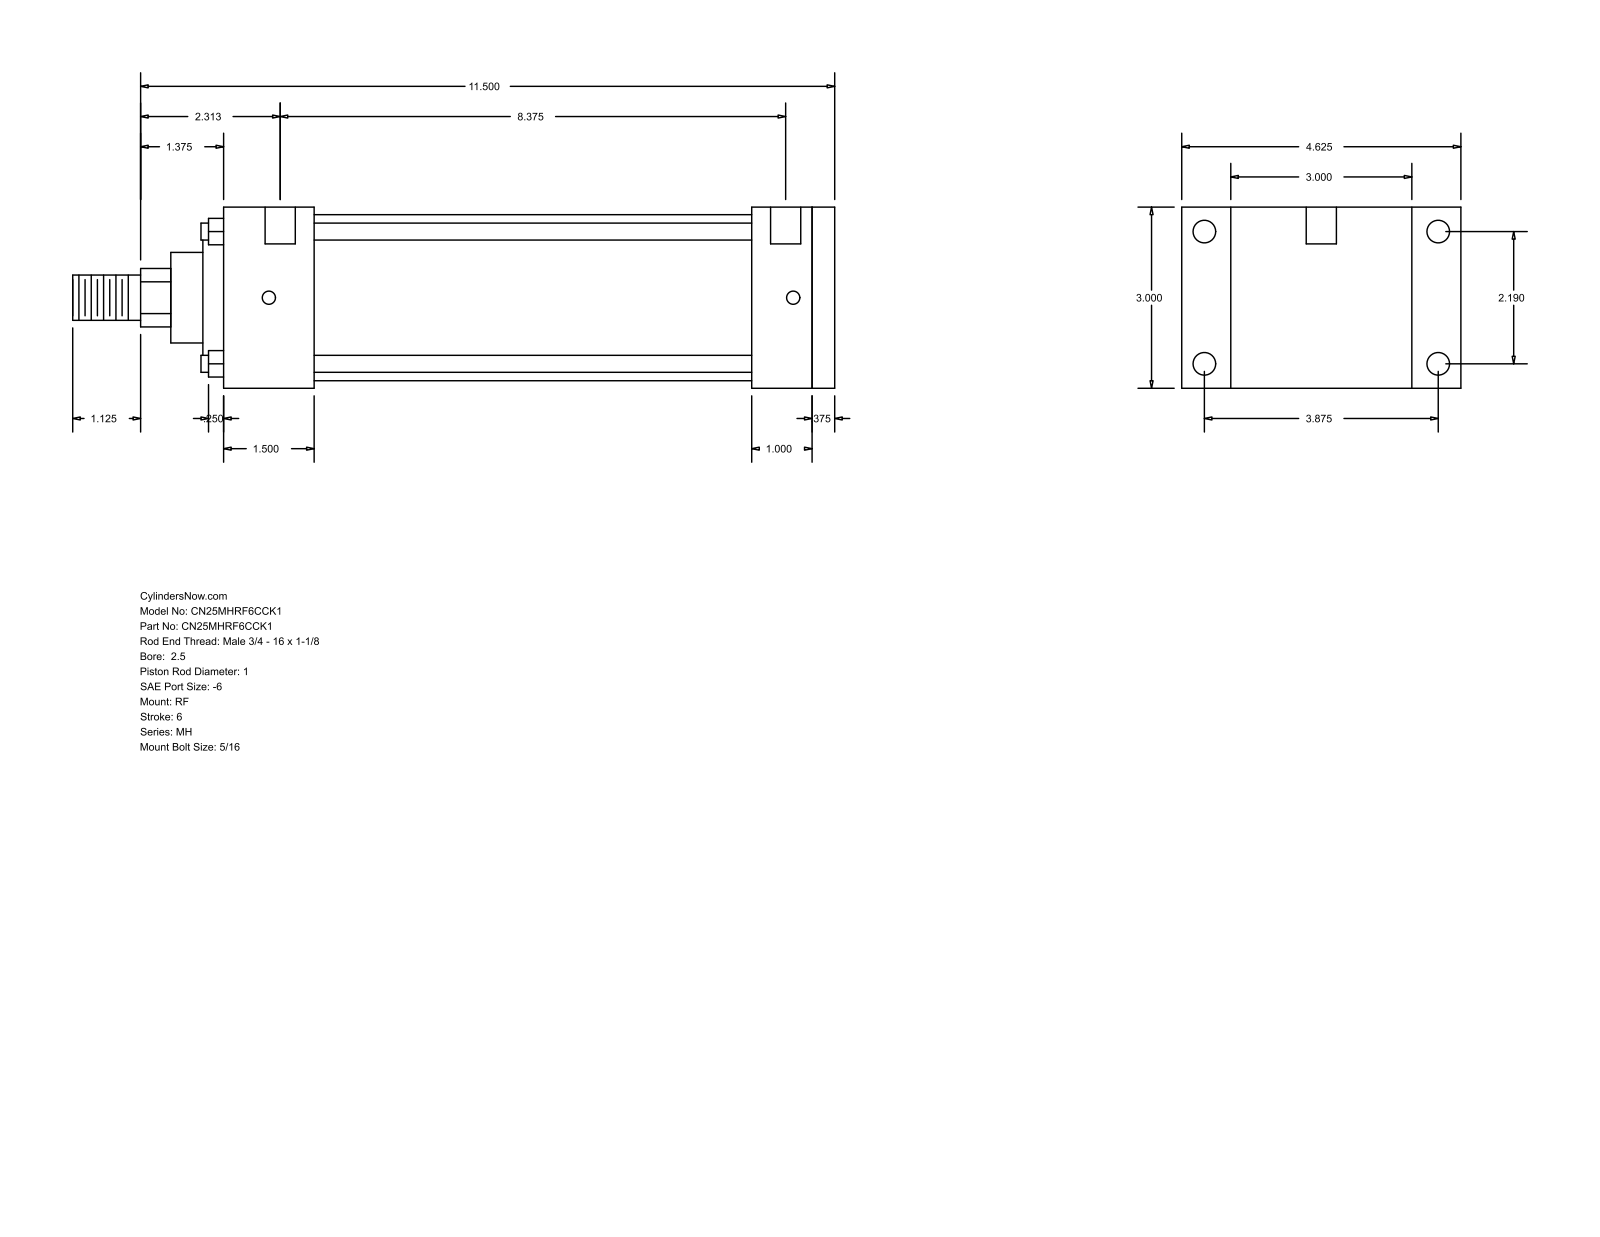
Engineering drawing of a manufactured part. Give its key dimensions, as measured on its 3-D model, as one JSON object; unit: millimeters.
{"part_name": "MH_RF__0250_1", "step_written_by": "GSSL Pune (CONFIG_CONTROL_DESIGN)", "units": "millimeters", "bodies": {"solids": 0, "faces": 94, "planar": 65, "cylindrical": 29, "other": 0}, "overall_size": [320.68, 117.47, 76.2], "round_holes": [[5.56, 4], [9.53, 4], [12.7, 2]], "round_bosses_or_shafts": [[7.14, 4], [69.85, 1], [60.33, 1], [38.1, 1], [25.4, 1], [19.05, 1]], "partial_cylinders_radius": [[12.29, 1]], "face_to_face_distances": [76.2, 9.53, 257.18, 247.65, 34.92, 25.39, 222.26, 38.11, 184.15, 209.54], "hole_center_spacings": [55.62, 98.42, 113.05, 220.66, 3.18, 4.76, 212.72, 215.9]}
